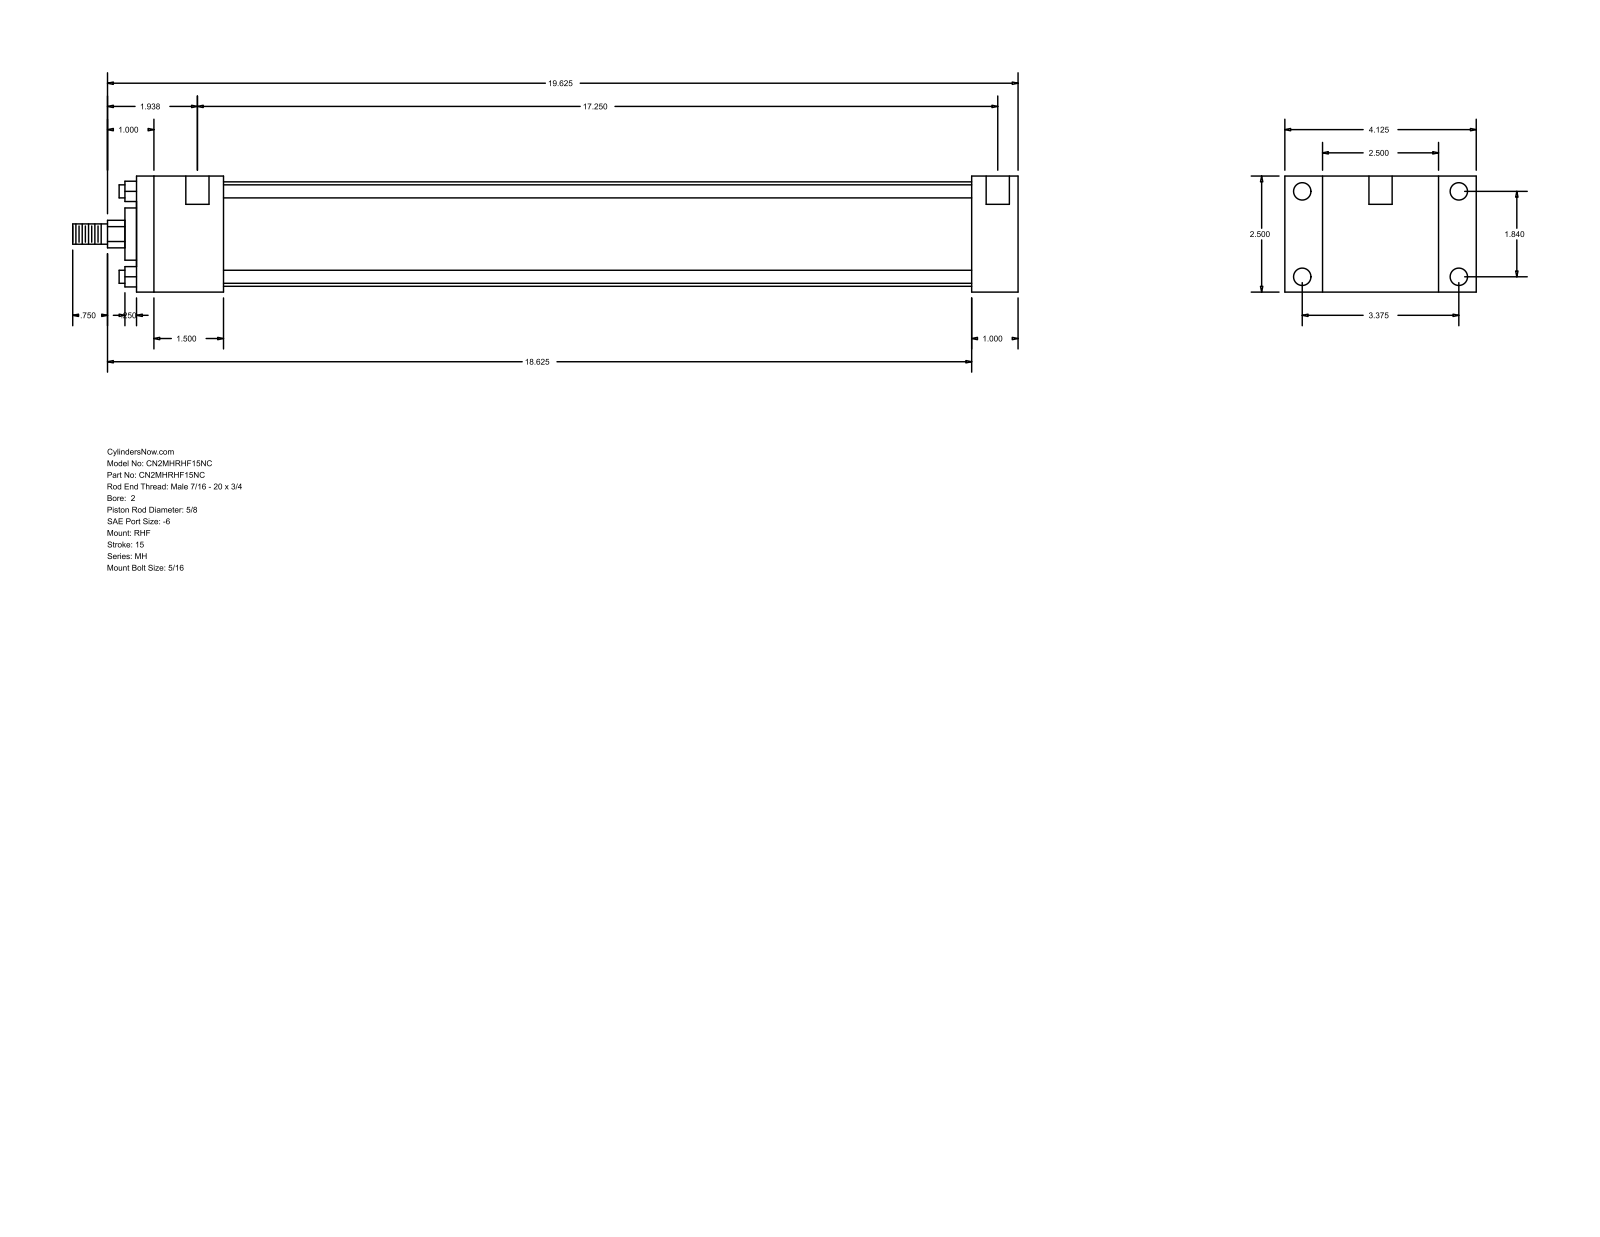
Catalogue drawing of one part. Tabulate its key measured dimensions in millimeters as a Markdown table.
| quantity | value |
| --- | --- |
| part name | MH_RHF__0200_0.625 |
| STEP written by | GSSL Pune (CONFIG_CONTROL_DESIGN) |
| units | millimeters |
| bodies | 0 solids, 88 faces (60 planar, 28 cylindrical, 0 other) |
| overall size | 517.52 × 104.78 × 63.5 |
| round holes (diameter × count) | 5.56 × 4, 9.53 × 4, 12.7 × 2 |
| round bosses / shafts (diameter × count) | 7.14 × 4, 57.15 × 1, 28.57 × 1, 15.88 × 1, 11.11 × 1 |
| partial cylindrical surfaces (radius × count) | 7.54 × 1 |
| main face-to-face distances | 63.5, 25.41, 20.64, 84.14, 457.19, 482.6, 104.78, 47.62, 409.57, 434.98 |
| hole center spacings | 46.74, 85.72, 97.63, 446.09, 3.18, 4.76, 438.15, 441.33 |
